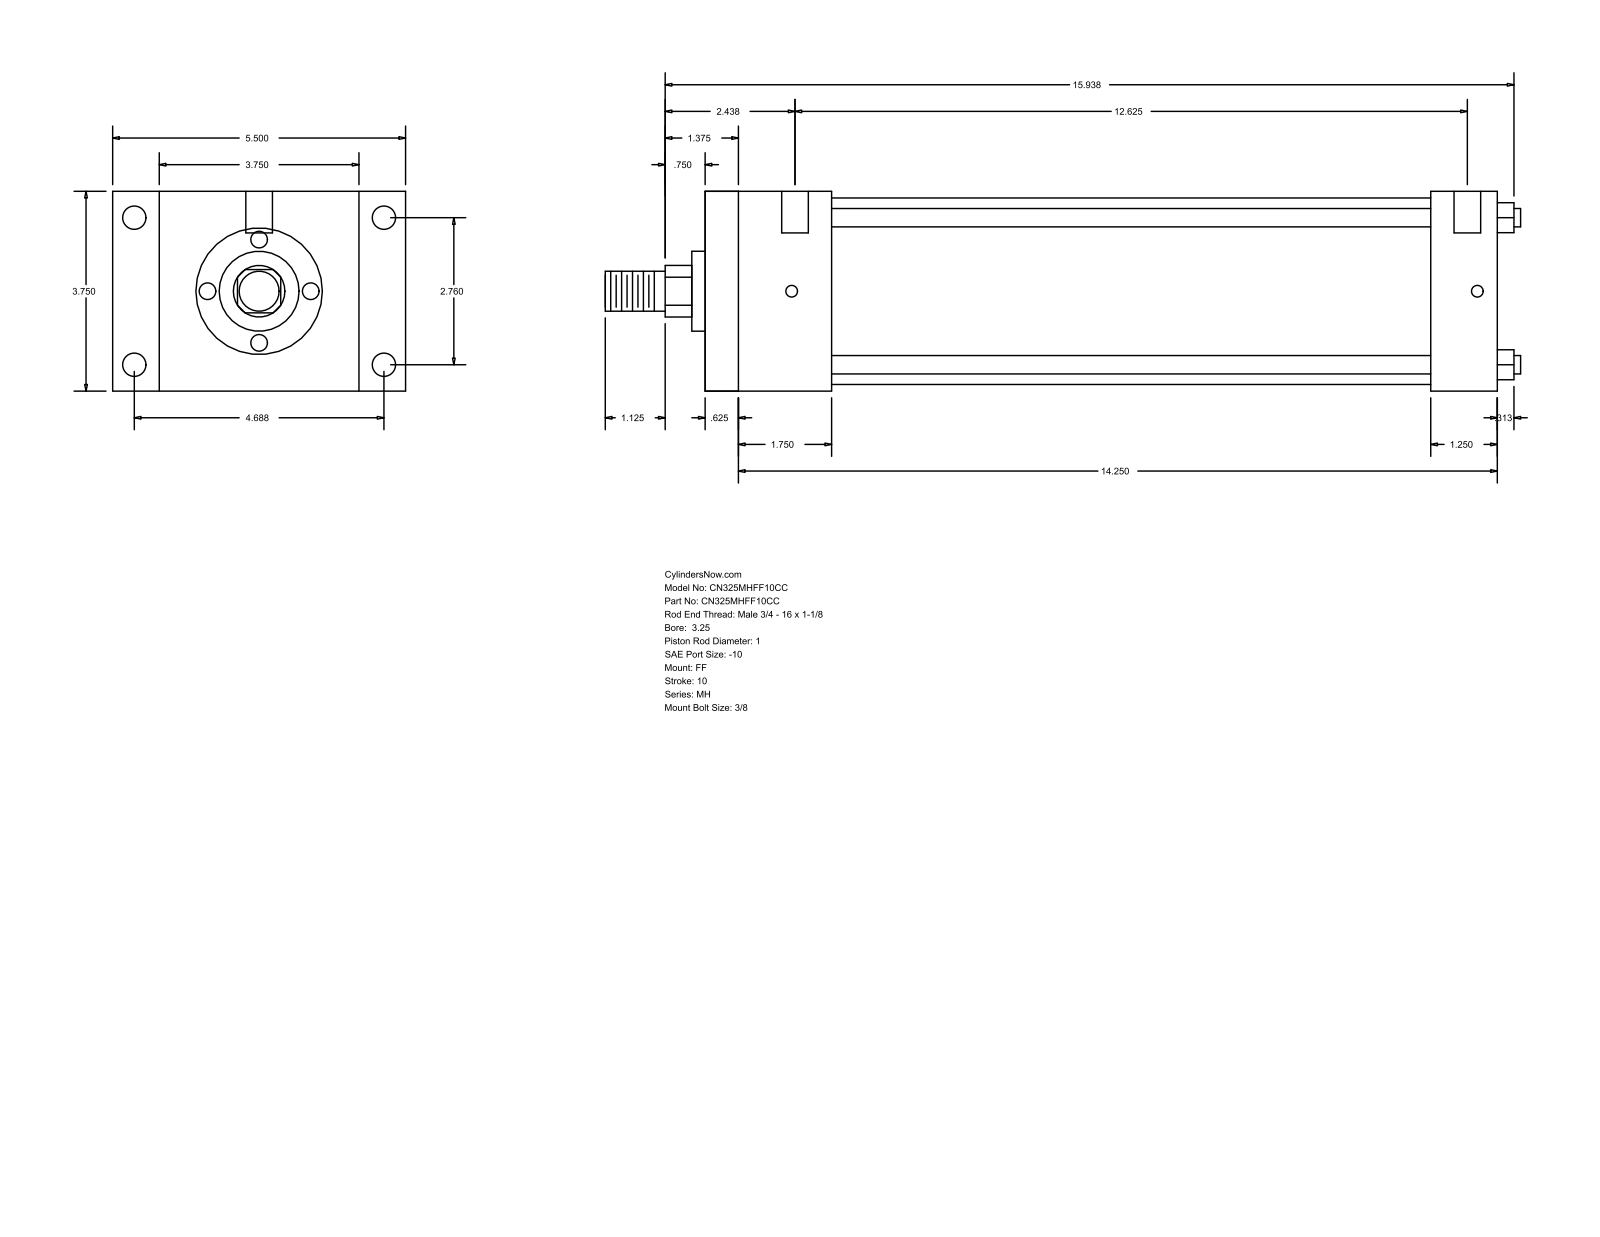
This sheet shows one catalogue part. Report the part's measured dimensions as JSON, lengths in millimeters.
{"part_name": "MH_FF__0325_1", "step_written_by": "GSSL Pune (CONFIG_CONTROL_DESIGN)", "units": "millimeters", "bodies": {"solids": 0, "faces": 92, "planar": 64, "cylindrical": 28, "other": 0}, "overall_size": [436.56, 139.7, 95.25], "round_holes": [[5.56, 4], [11.13, 4], [12.7, 2]], "round_bosses_or_shafts": [[8.76, 4], [88.9, 1], [38.1, 1], [25.4, 1], [19.05, 1]], "partial_cylinders_radius": [[12.29, 1]], "face_to_face_distances": [95.24, 377.83, 15.87, 361.96, 22.23, 117.47, 346.07, 330.2, 31.76, 60.33], "hole_center_spacings": [70.1, 119.06, 138.16, 327.02, 1.58, 4.76, 320.68, 322.26]}
